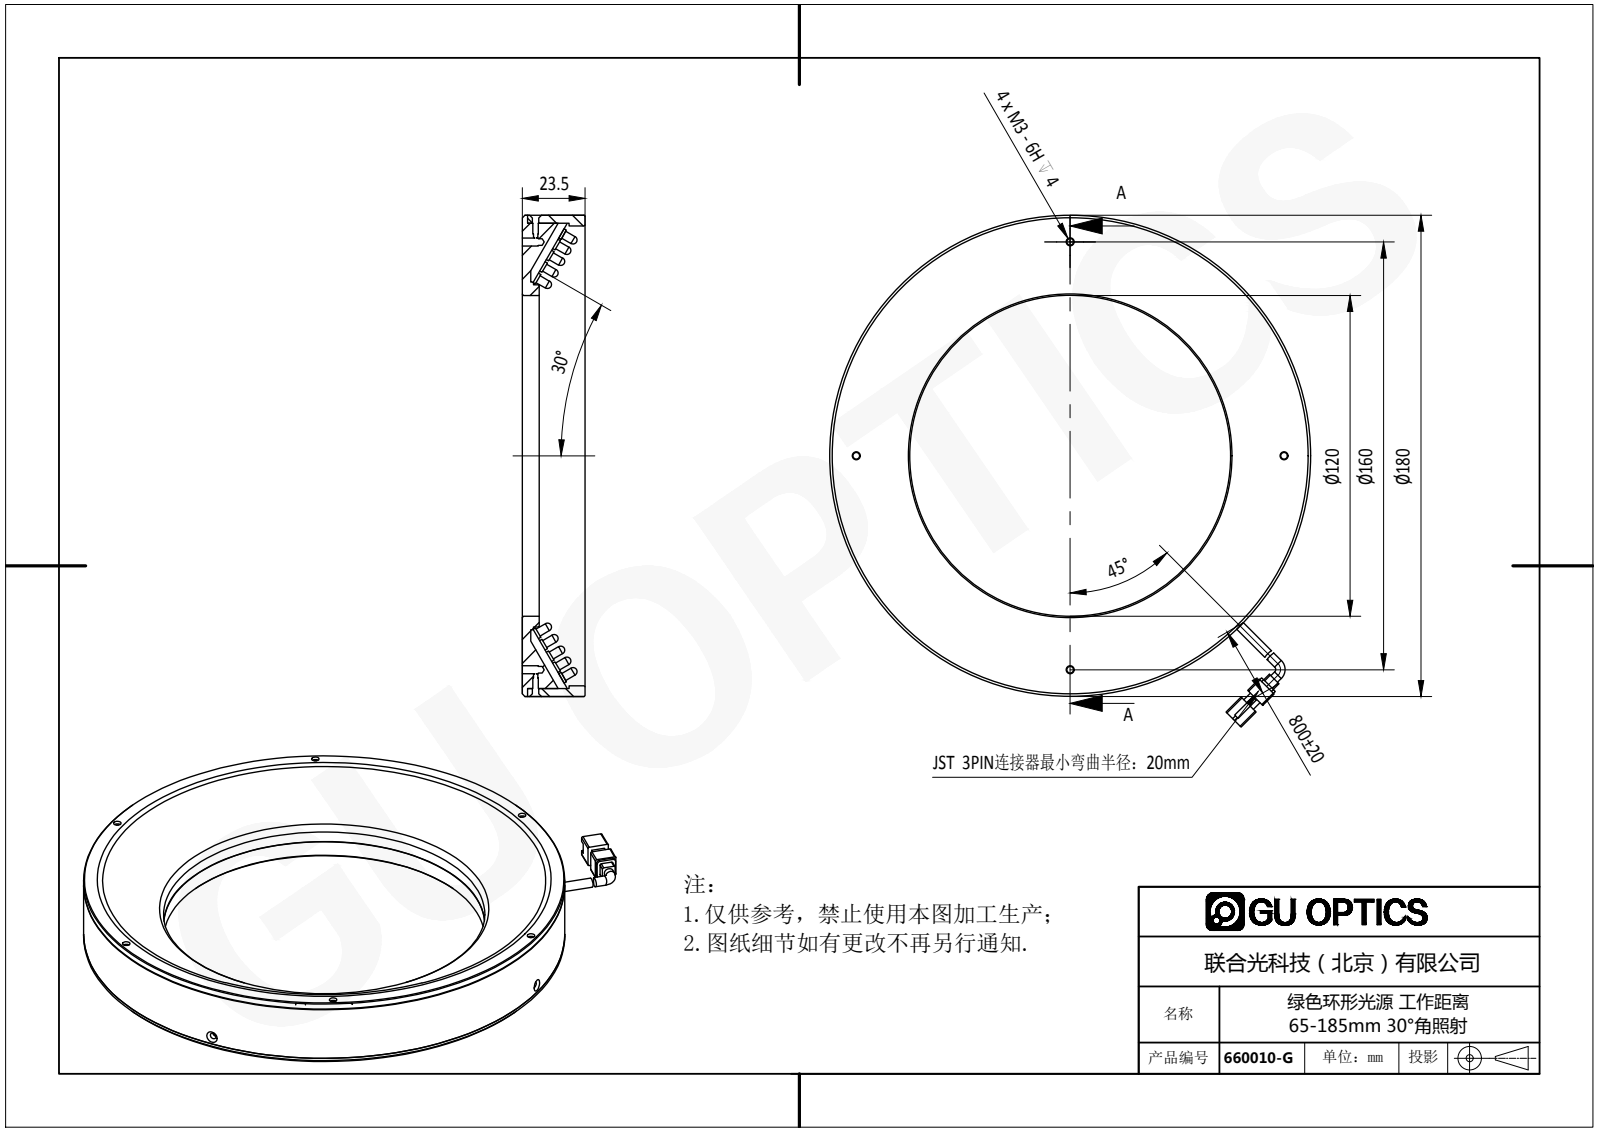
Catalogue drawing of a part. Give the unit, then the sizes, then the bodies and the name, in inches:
Units: inches
Overall size (bounding box): 7.538 × 7.087 × 1.024
Round holes (diameter × count): ⌀0.063 ×8, ⌀0.049 ×6, ⌀0.059 ×6, ⌀0.11 ×6, ⌀0.098 ×4, ⌀0.118 ×4, ⌀0.138 ×4, ⌀0.079 ×2, ⌀0.094 ×2, ⌀0.142 ×1, ⌀4.724 ×1, ⌀4.732 ×1
Round bosses / shafts (diameter × count): ⌀0.15 ×320, ⌀0.118 ×320, ⌀0.138 ×2, ⌀7.087 ×1, ⌀6.85 ×1, ⌀5.118 ×1, ⌀5.039 ×1, ⌀4.929 ×1
Partial cylindrical surfaces — rounded edges, fillets, slot ends (radius × count): R0.02 ×8, R0.039 ×4, R0.354 ×1
Main face-to-face distances: 0.925, 0.079, 0.846, 0.098, 1.024, 0.945, 0.039, 0.048, 0.127, 0.798
Hole centre spacings: 3.445, 5.967, 1.73, 3.15, 3.307, 4.454, 4.668, 5.713
Volume: 11.86 in³ · Surface area: 246.8 in²
Bodies: 326 solids, 5763 faces (3930 planar, 1439 cylindrical, 394 other)
Part name (STEP PRODUCT): 660010-G
STEP written by: SolidWorks 2016 (AUTOMOTIVE_DESIGN)
